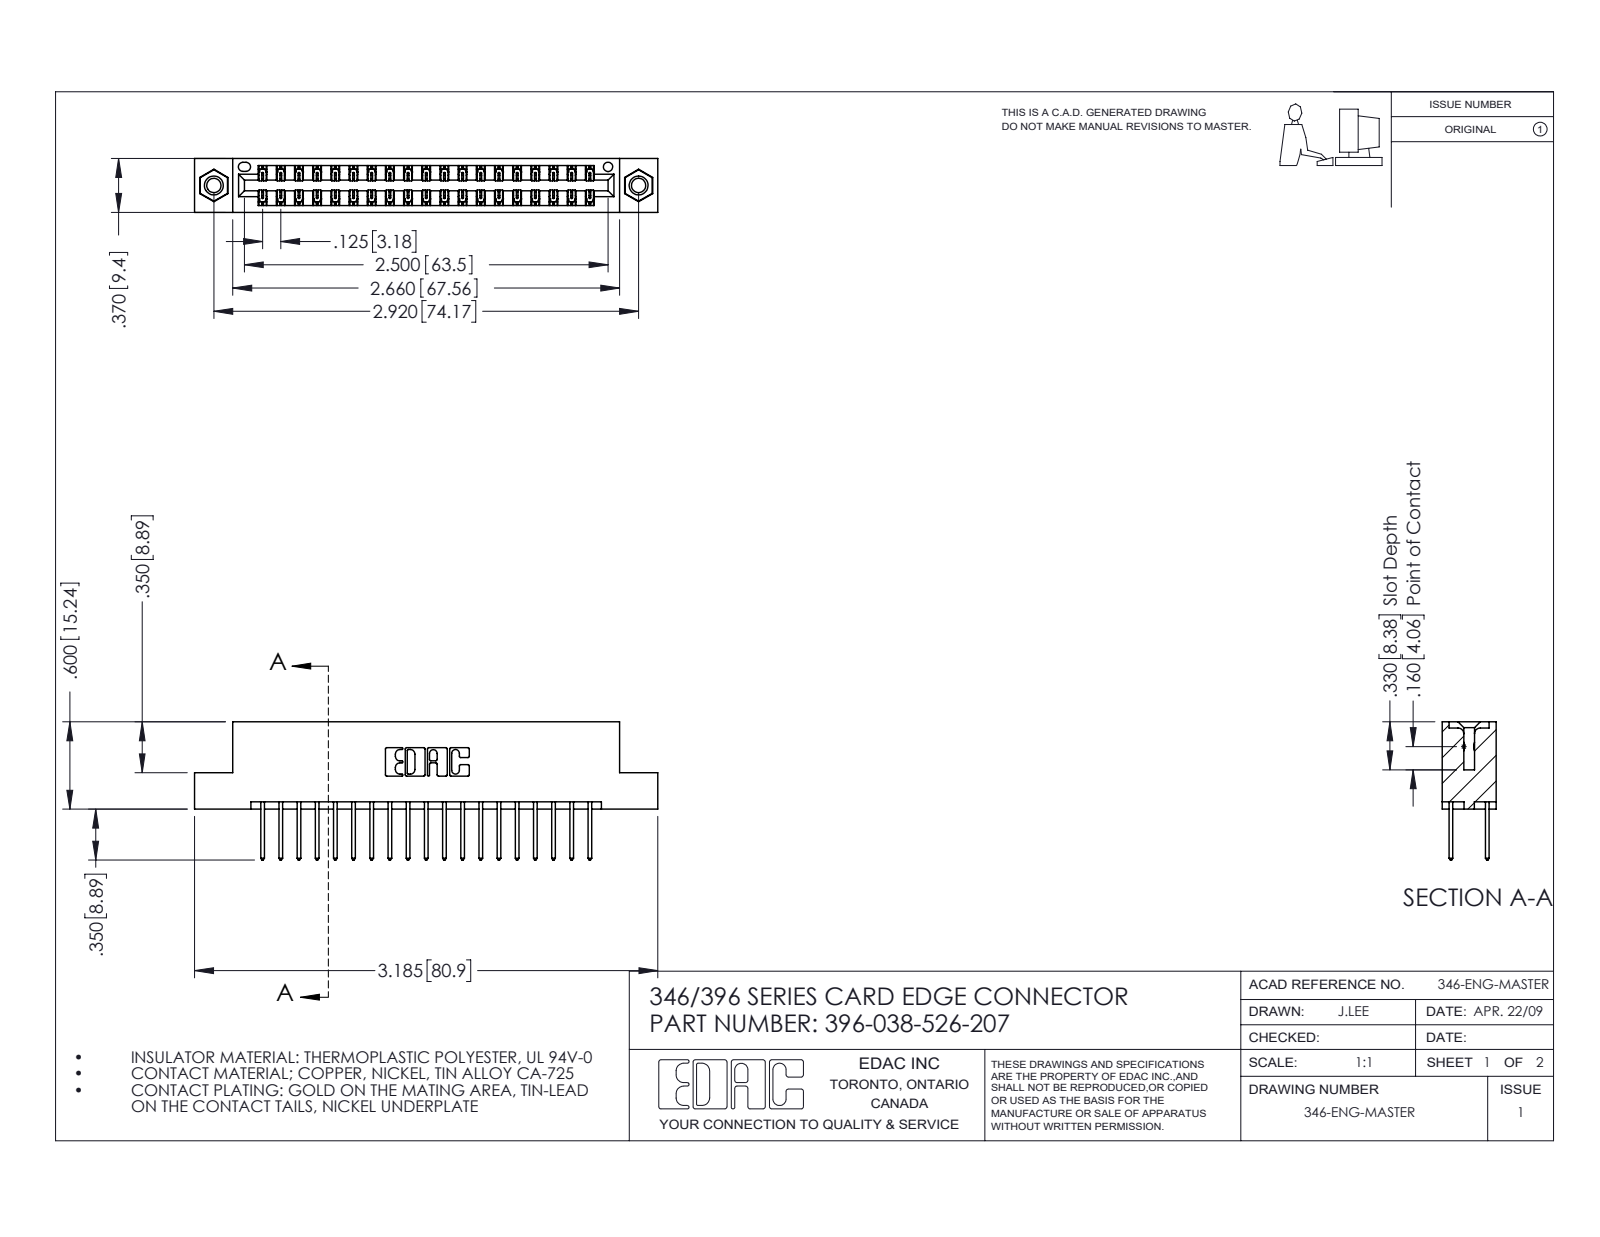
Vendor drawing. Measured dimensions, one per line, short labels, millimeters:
name: 396-038-526-207; 345-250-001_345-250-005-103; 345-292-001_345-293-126; 346 Part_Flush Mounting Lugs - 0.156 Dia-TI
written by: SolidWorks 2016 (CONFIG_CONTROL_DESIGN)
unit: mm
bodies: 41 solids, 2158 faces (1438 planar, 704 cylindrical, 16 other)
size: 80.9 × 24.1 × 9.4
volume: 7 750 mm³; area: 10 620 mm²
holes: 2× ⌀2.5, 2× ⌀3.2, 2× ⌀4, 1× ⌀1.6
bosses: 2× ⌀3.9
rounds: 57× R0.2, 38× R0.3, 22× R0.3, 6× R0.2, 6× R0.8, 3× R0.7, 2× R0.4, 2× R0.6
face distances: 1.2, 8.2, 6.4, 9.4, 1.8, 7.6, 0.6, 7, 3.8, 5.6
hole spacings: 6.2, 68.9, 74.2
